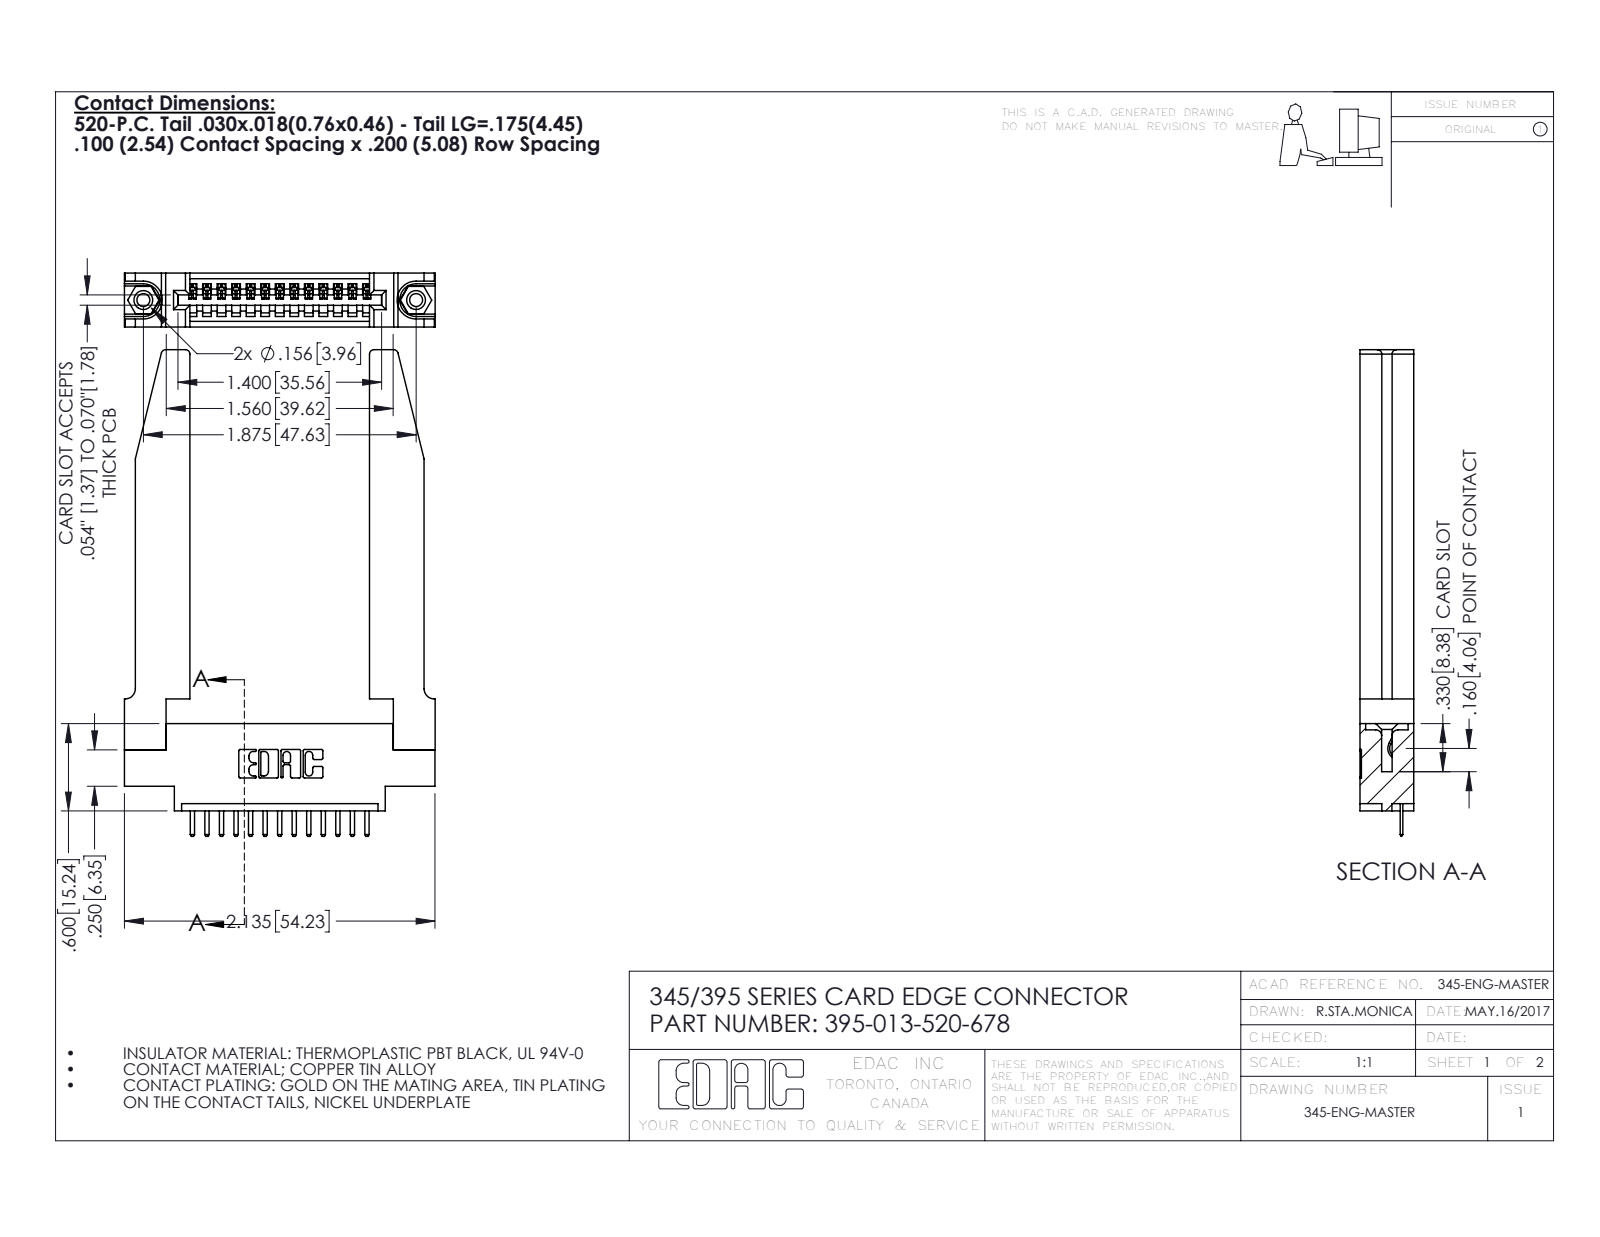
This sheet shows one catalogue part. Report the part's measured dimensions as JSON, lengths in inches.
{"part_name": "345-250-001_345-250-001-102; 395-013-520-678; 345-220-078_345-220-078; 345-292-001_345-293-120 (+1 more)", "step_written_by": "SolidWorks 2016 (CONFIG_CONTROL_DESIGN)", "units": "inches", "bodies": {"solids": 18, "faces": 1170, "planar": 772, "cylindrical": 346, "other": 52}, "overall_size": [3.345, 2.136, 0.37], "volume_in3": 0.765, "surface_area_in2": 19.82, "round_holes": [[0.089, 2], [0.125, 2], [0.156, 2], [0.064, 1]], "round_bosses_or_shafts": [[0.155, 2]], "partial_cylinders_radius": [[0.01, 28], [0.006, 26], [0.01, 22], [0.03, 8], [0.007, 6], [0.031, 6], [0.026, 3], [0.031, 2]], "face_to_face_distances": [0.37, 0.072, 0.298, 0.148, 0.15, 0.22, 0.077, 1.235, 0.123, 0.098], "hole_center_spacings": [0.27, 1.643, 1.875]}
